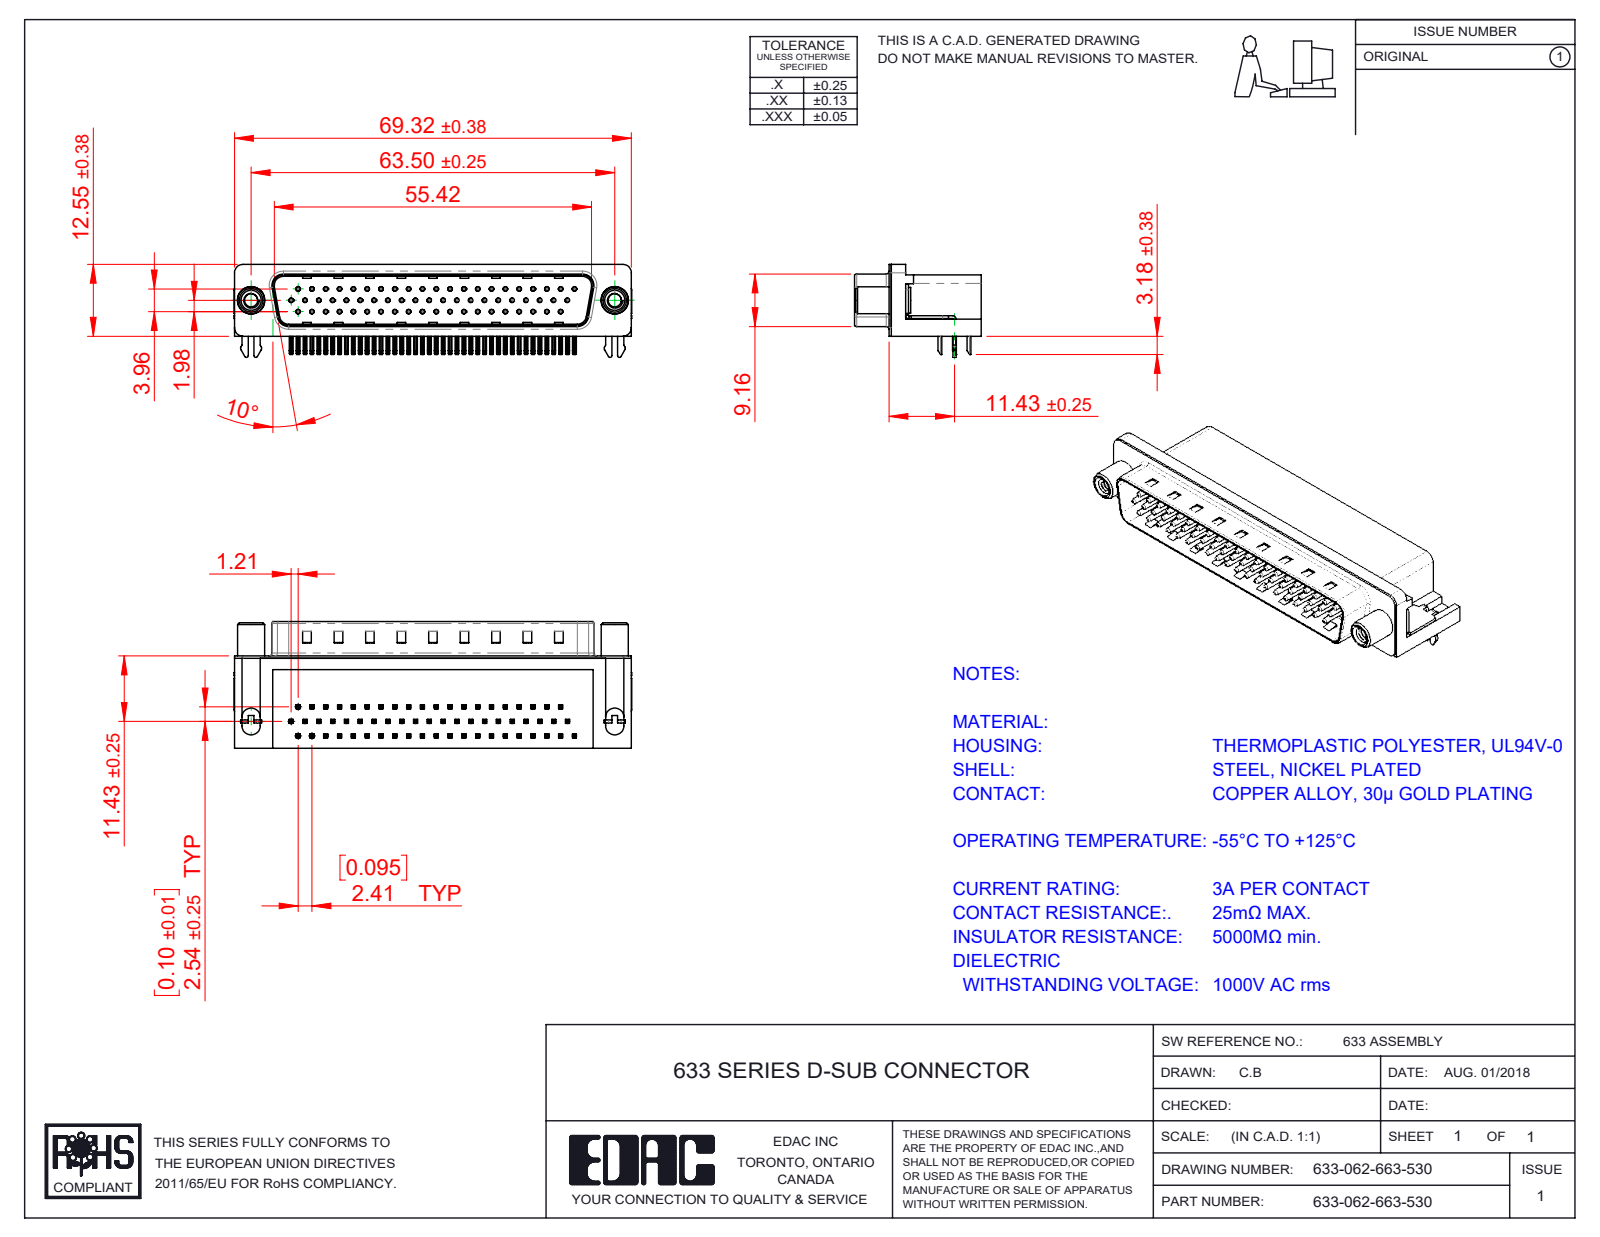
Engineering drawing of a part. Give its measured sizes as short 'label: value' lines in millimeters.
name: 633 Round Threaded Standoff; 633 Contact Bottom; 633 Contact Middle; 633-062-663-530 (+4 more)
written by: SolidWorks 2016 (CONFIG_CONTROL_DESIGN)
unit: mm
bodies: 68 solids, 5110 faces (3237 planar, 1458 cylindrical, 415 other)
size: 69.4 × 22.1 × 16.25
volume: 11 144 mm³; area: 13 609 mm²
holes: 62× ⌀0.35, 62× ⌀0.8, 2× ⌀2.3, 2× ⌀3.1, 2× ⌀4, 2× ⌀4.8, 2× ⌀5
bosses: 62× ⌀0.75, 2× ⌀4.9, 2× ⌀4.7, 2× ⌀4.5, 2× ⌀3.85
rounds: 248× R0.25, 124× R0.12, 16× R1, 14× R0.5, 8× R1.6, 7× R1.5, 4× R0.32, 4× R0.9
face distances: 0.4, 10.35, 15.7, 8.76, 2.9, 2.5, 2.54, 2.1, 8.36, 10.46
hole spacings: 2.41, 4.82, 7.24, 9.65, 14.48, 16.89, 4.83, 7.23
